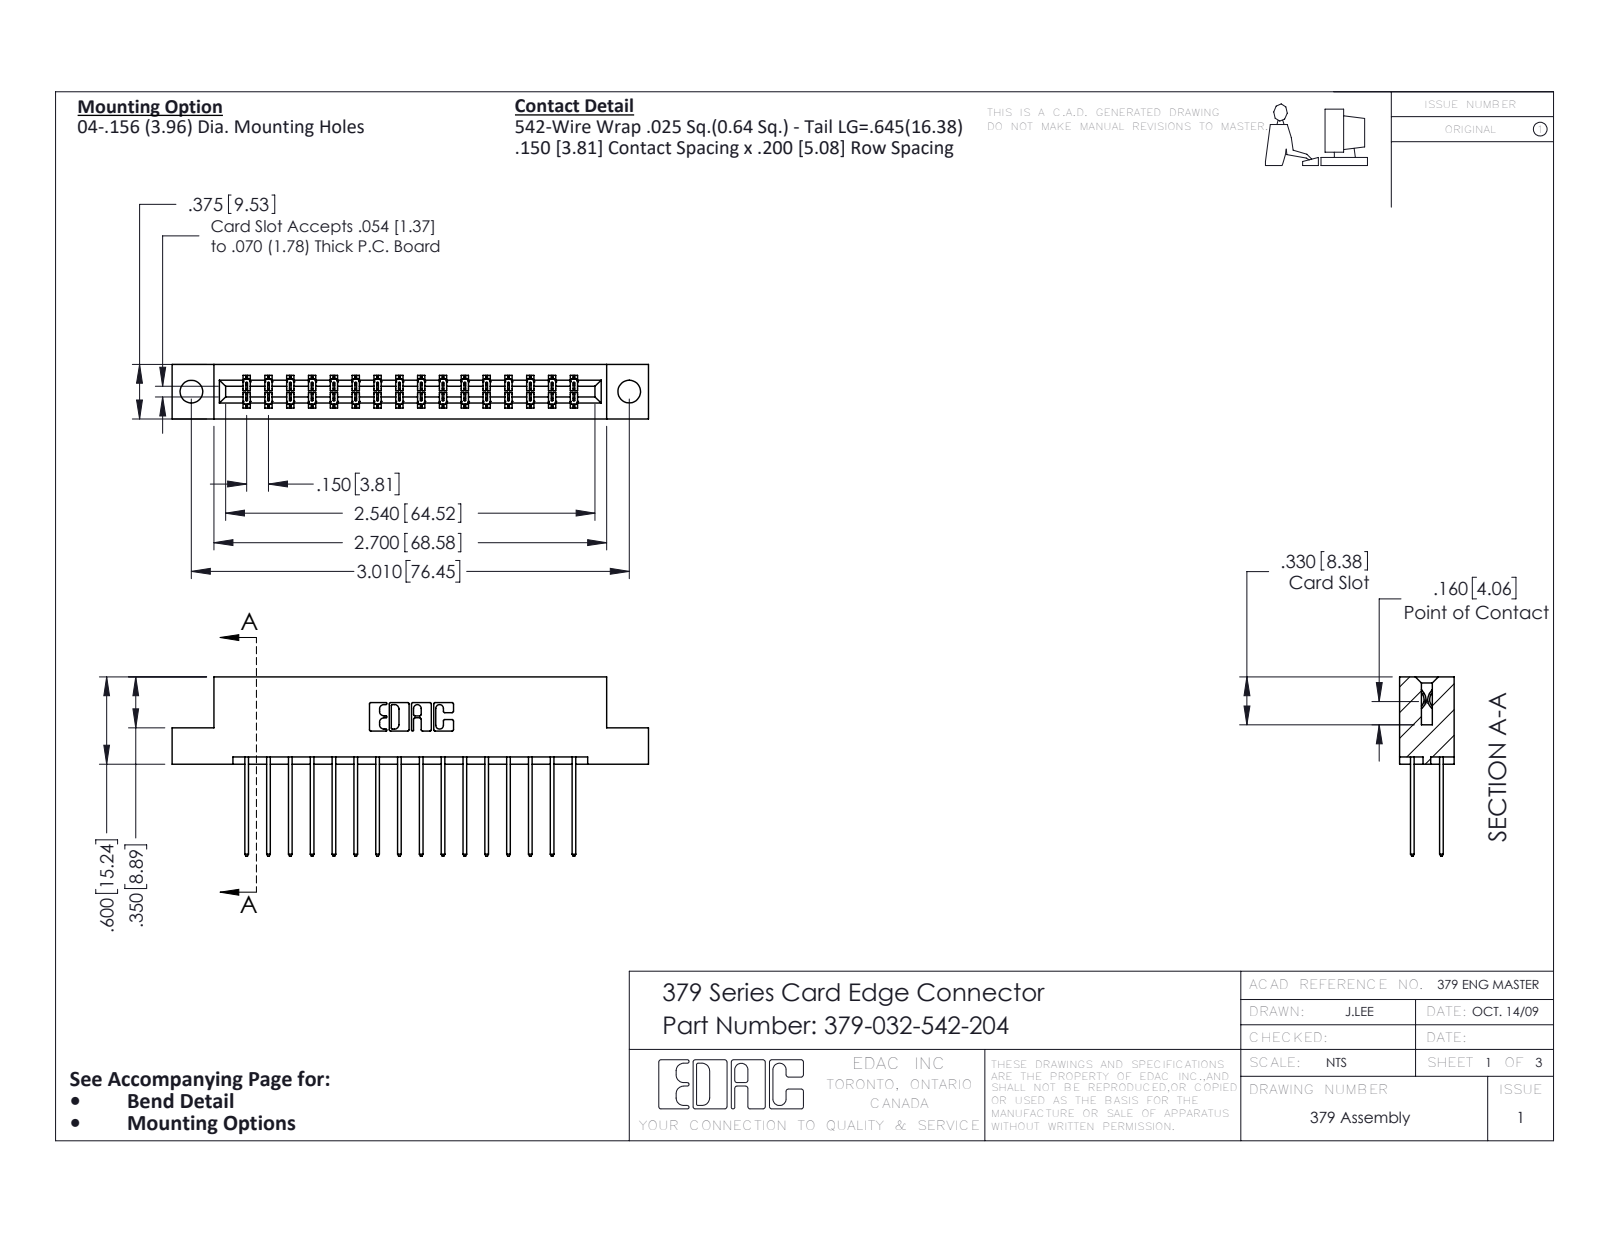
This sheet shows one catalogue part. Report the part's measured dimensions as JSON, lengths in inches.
{"part_name": "345-292-001_345-293-142; 379-032-542-204; 379 Part_Flush - .156 Dia - TH", "step_written_by": "SolidWorks 2020 (CONFIG_CONTROL_DESIGN)", "units": "inches", "bodies": {"solids": 33, "faces": 1778, "planar": 1222, "cylindrical": 556, "other": 0}, "overall_size": [3.275, 1.232, 0.375], "volume_in3": 0.525, "surface_area_in2": 15.43, "round_holes": [[0.156, 2]], "partial_cylinders_radius": [[0.006, 63], [0.01, 32], [0.01, 22], [0.007, 6], [0.031, 6], [0.026, 3], [0.014, 2], [0.022, 2]], "face_to_face_distances": [0.3, 0.075, 0.2, 0.1, 0.375, 0.275, 0.15, 0.05, 0.6, 0.025], "hole_center_spacings": [3.01]}
